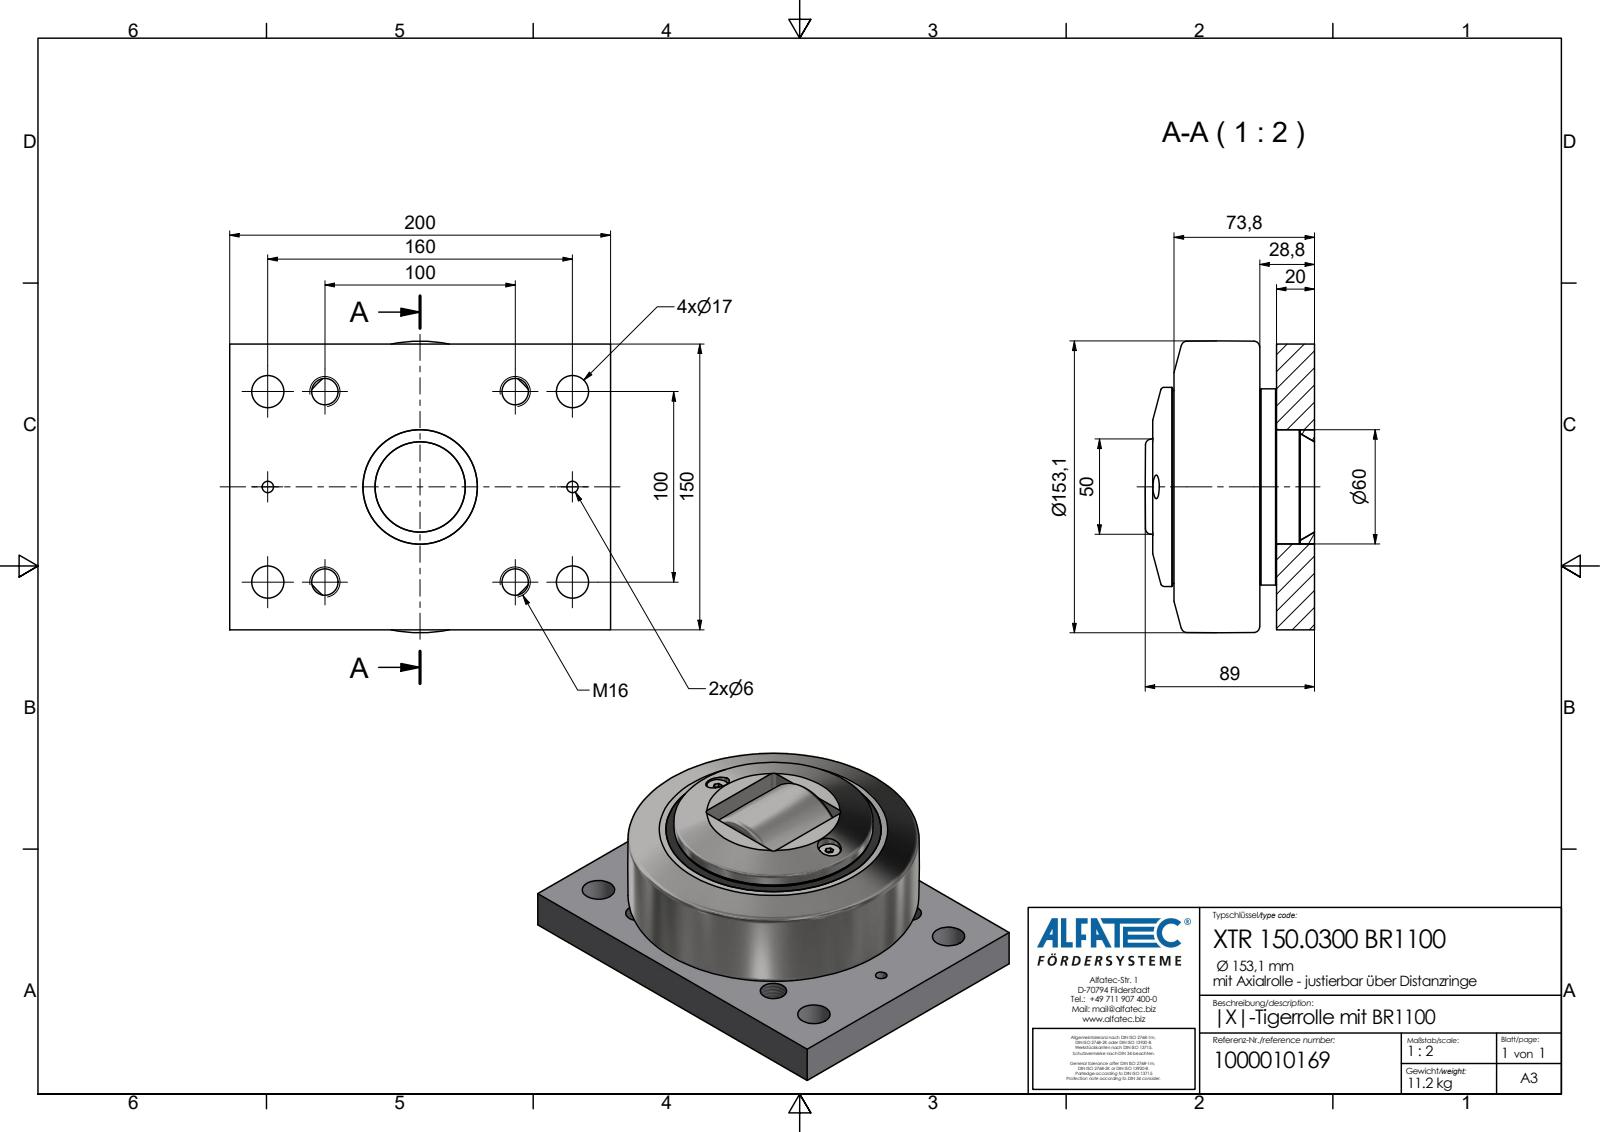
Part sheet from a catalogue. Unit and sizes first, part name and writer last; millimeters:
Units: millimetres
Overall size (bounding box): 200 × 153.1 × 89
Round holes (diameter × count): ⌀13.84 ×4, ⌀17 ×4, ⌀6 ×2, ⌀12.4 ×2
Round bosses / shafts (diameter × count): ⌀11.7 ×2, ⌀104.5 ×1, ⌀103 ×1, ⌀101.4 ×1, ⌀101.2 ×1
Partial cylindrical surfaces — rounded edges, fillets, slot ends (radius × count): R2 ×4, R14.35 ×1, R17.35 ×1, R20.35 ×1
Main face-to-face distances: 20, 28.8, 8.8, 150, 73.8, 53.8, 45, 200, 85, 65
Hole centre spacings: 100, 30, 50, 50.72, 58.31, 63.11, 104.27, 104.4
Volume: 1 532 000 mm³ · Surface area: 128 990 mm²
Bodies: 1 solid, 89 faces (47 planar, 28 cylindrical, 14 other)
Part name (STEP PRODUCT): XTR 150.0300 BR1100_Kontur
STEP written by: Autodesk Inventor 2020 (AP242_MANAGED_MODEL_BASED_3D_ENGINEERING_MIM_LF)
